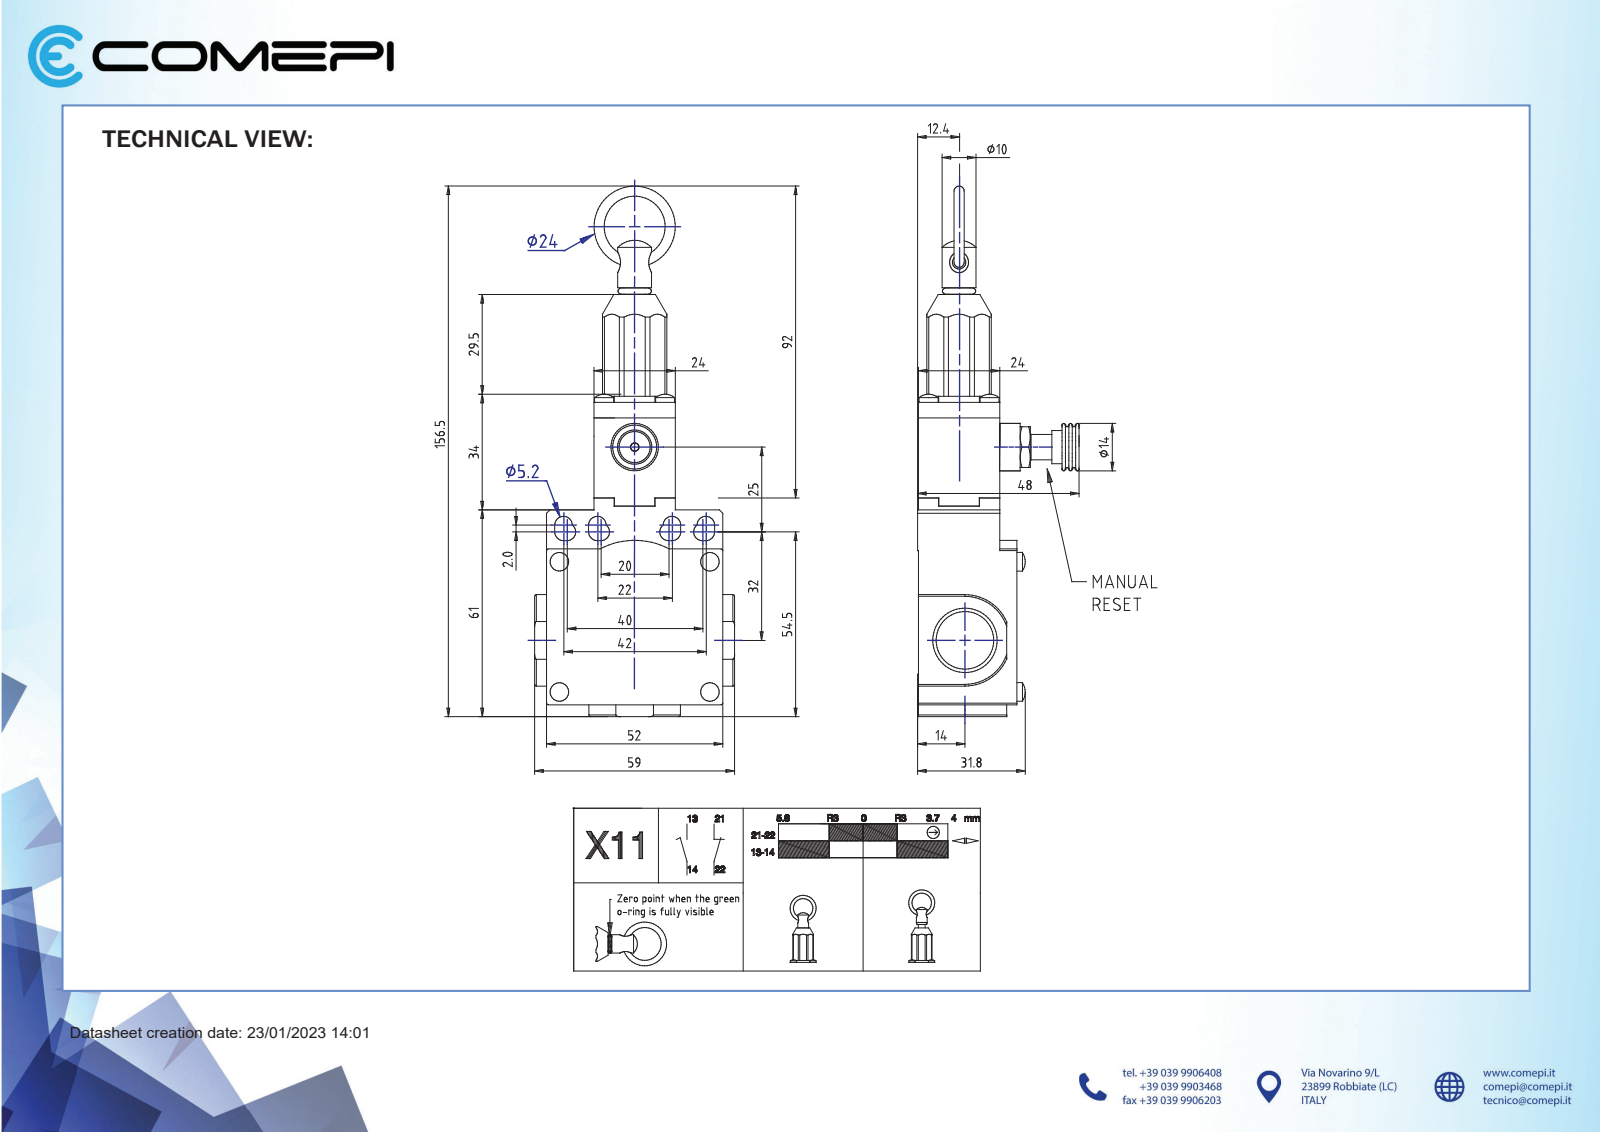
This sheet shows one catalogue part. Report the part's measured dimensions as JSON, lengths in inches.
{"part_name": "SDM2K9800X11", "step_written_by": "SolidWorks 2021 (AUTOMOTIVE_DESIGN)", "units": "inches", "bodies": {"solids": 9, "faces": 353, "planar": 216, "cylindrical": 89, "other": 48}, "overall_size": [6.141, 2.323, 1.683], "volume_in3": 6.889, "surface_area_in2": 43.3, "round_holes": [[0.118, 4], [0.669, 2], [0.748, 2], [0.138, 1], [0.157, 1], [0.236, 1], [0.276, 1]], "round_bosses_or_shafts": [[0.217, 4], [0.189, 4], [0.129, 4], [0.394, 1], [0.354, 1], [0.315, 1], [0.264, 1], [0.248, 1]], "partial_cylinders_radius": [[0.102, 12], [0.02, 10], [0.039, 9], [0.118, 4], [0.531, 2], [0.4, 1], [0.866, 1]], "face_to_face_distances": [1.144, 0.945, 1.496, 0.551, 0.138, 0.199, 2.047, 0.098, 0.236, 2.185], "hole_center_spacings": [0.728, 0.469, 0.566, 1.03, 4.321]}
